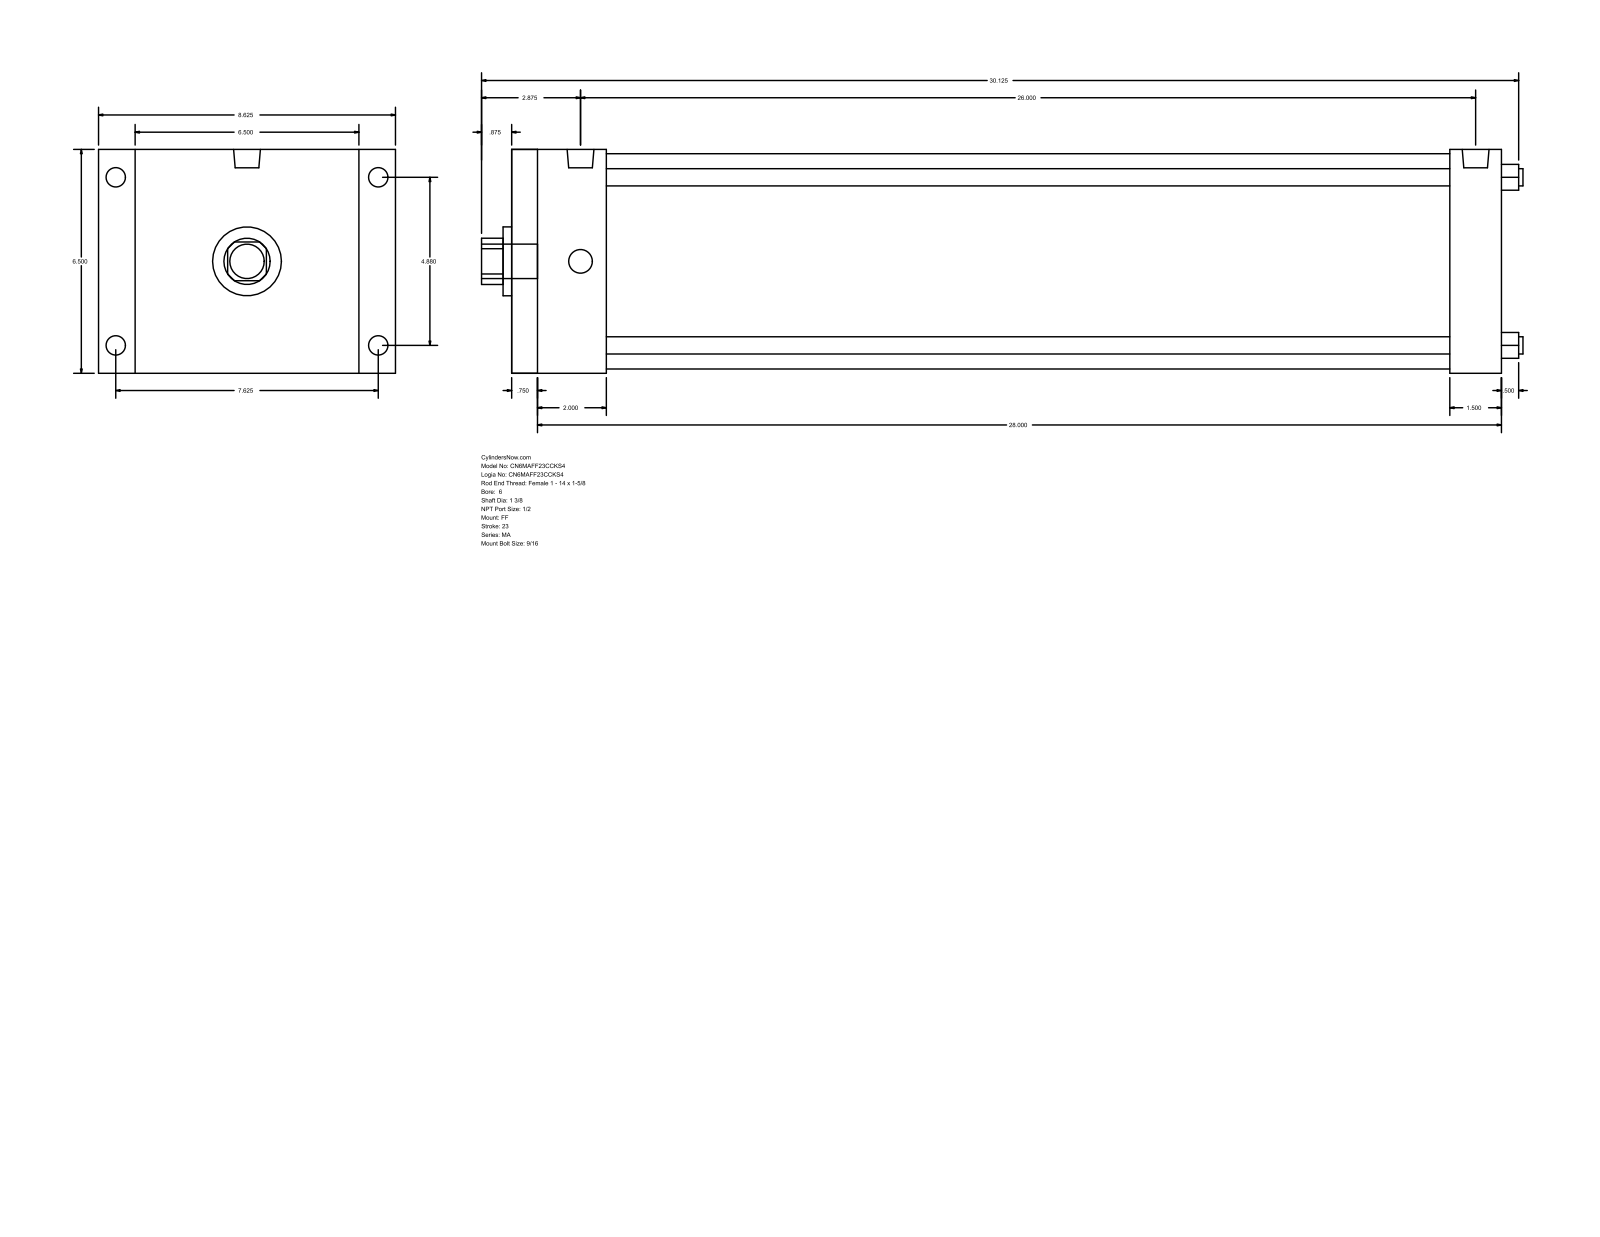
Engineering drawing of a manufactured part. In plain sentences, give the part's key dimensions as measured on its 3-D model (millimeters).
The part is named "MA_FF__0600_1.375". Its 3-D file was written by "GSSL Pune (CONFIG_CONTROL_DESIGN)". It is 0 solids with 92 faces: 64 planar, 28 cylindrical and 0 other. Overall it measures 768.35 by 219.07 by 165.1 millimeters. Round holes: 4 of diameter 12.7, 1 of diameter 34.92, 1 of diameter 50.8, 1 of diameter 158.75. Round bosses or shafts: 4 of diameter 17.46, 4 of diameter 14.29, 2 of diameter 19.77, 1 of diameter 25.4. Partial cylindrical surfaces (rounded edges, fillets, slot ends): 1 of radius 17.06. The main face-to-face distances are 165.1, 730.25, 15.87, 714.38, 38.1, 66.67, 50.8, 663.58, 692.15, 676.28. The hole center spacings are 87.65, 123.96, 175.31.
